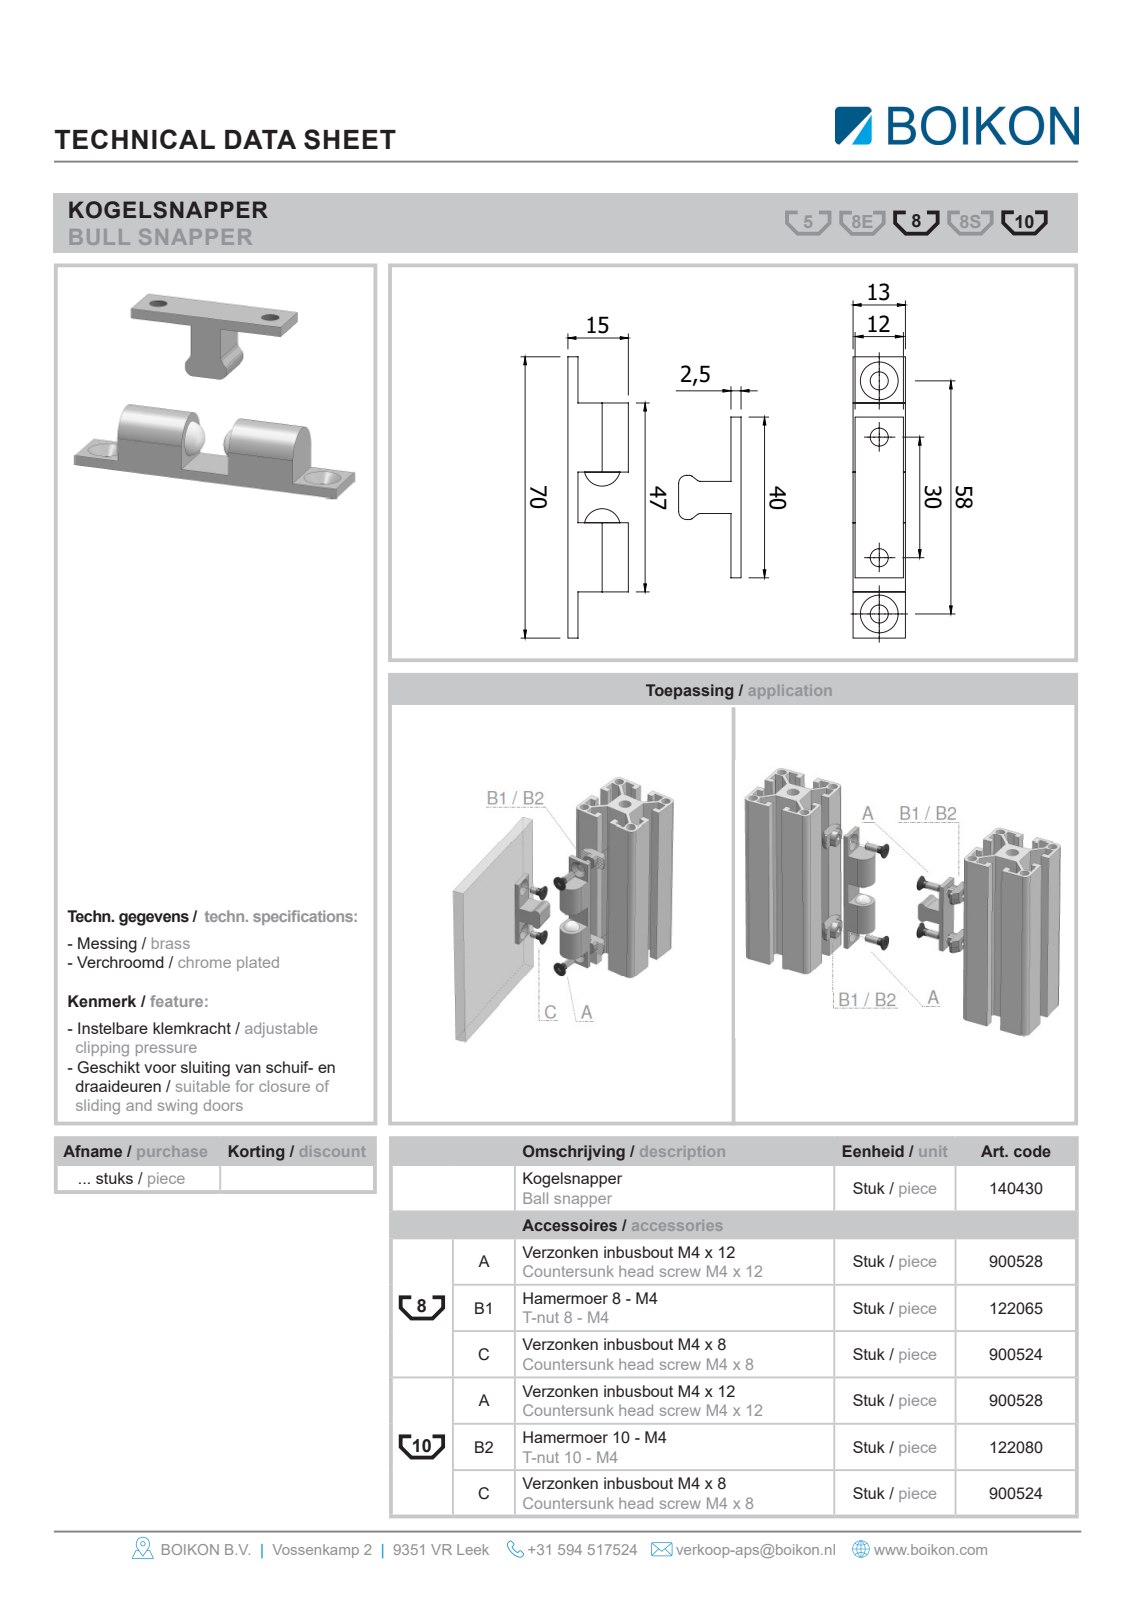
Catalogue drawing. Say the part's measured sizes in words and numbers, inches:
The part is named "Root; 140430KogelsnapperBOIKON; ISO 10642-M4x12-8.8Countersunk head bolts0". Its 3-D file was written by "HiCAD 2013 1802.4 Build 509 (AUTOMOTIVE_DESIGN)". It is 6 solids with 100 faces: 62 planar, 24 cylindrical and 14 other. Overall it measures 2.756 by 1.457 by 0.512 inches. Its volume is 0.629 cubic inches and its surface area 9.698 square inches. Round holes: 4 of diameter 0.177. Round bosses or shafts: 4 of diameter 0.315, 4 of diameter 0.157, 4 of diameter 0.124. Partial cylindrical surfaces (rounded edges, fillets, slot ends): 4 of radius 0.039, 2 of radius 0.079, 1 of radius 0.256. The main face-to-face distances are 0.098, 0.61, 0.512, 0.709, 0.492, 0.02, 0.472, 1.083, 0.768, 0.677. The hole center spacings are 0.551, 1.732, 1.181, 2.283.
